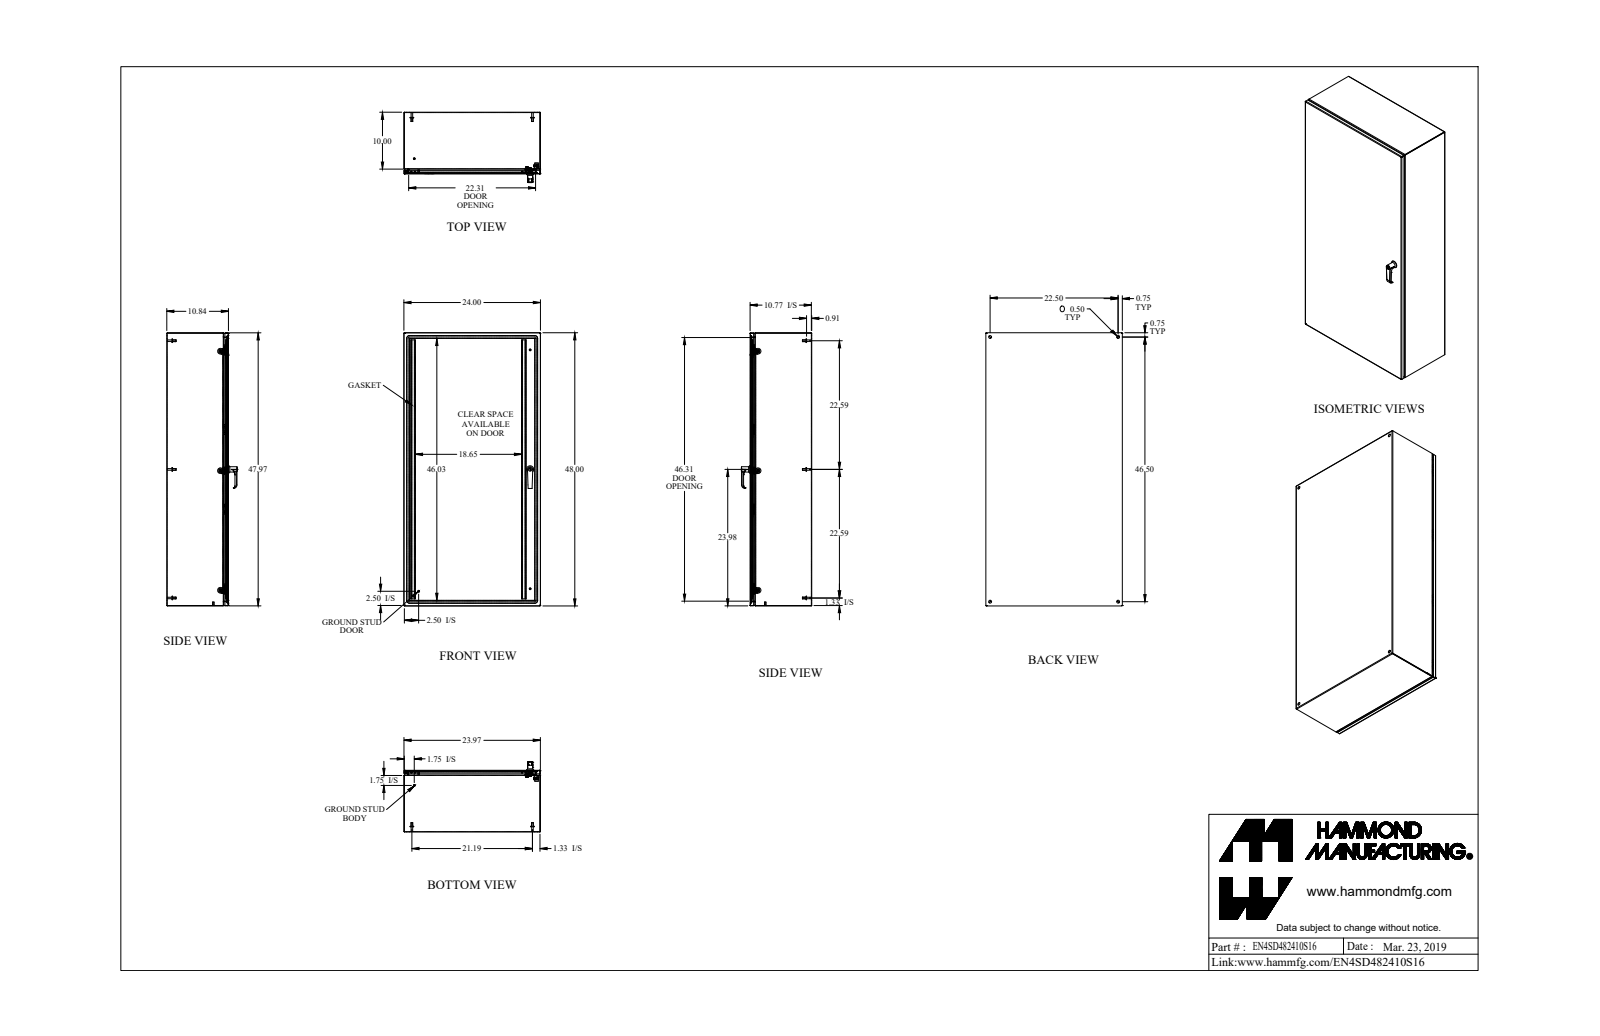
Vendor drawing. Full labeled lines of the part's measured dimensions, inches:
Part name (STEP PRODUCT): EN4SD482410S16
STEP written by: SolidWorks 2018 (AUTOMOTIVE_DESIGN)
Units: inches
Bodies: 53 solids, 1467 faces (632 planar, 536 cylindrical, 299 other)
Overall size (bounding box): 48 × 24 × 12.372
Volume: 319.5 in³ · Surface area: 8 871 in²
Round holes (diameter × count): ⌀0.176 ×6, ⌀0.5 ×4, ⌀0.196 ×3, ⌀0.25 ×3, ⌀0.265 ×3, ⌀0.413 ×3, ⌀0.256 ×2, ⌀0.313 ×2, ⌀0.394 ×2, ⌀0.172 ×1, ⌀0.24 ×1, ⌀0.242 ×1
Round bosses / shafts (diameter × count): ⌀0.313 ×8, ⌀0.25 ×7, ⌀0.625 ×6, ⌀0.375 ×6, ⌀0.275 ×6, ⌀0.156 ×6, ⌀1 ×3, ⌀0.63 ×2
Partial cylindrical surfaces — rounded edges, fillets, slot ends (radius × count): R0.036 ×20, R0.108 ×20, R0.03 ×15, R0.01 ×12, R0.048 ×12, R0.006 ×8, R0.04 ×8, R0.062 ×8
Main face-to-face distances: 0.072, 10.77, 10.698, 10.842, 23.928, 23.856, 24, 0.072, 47.928, 47.928
Hole centre spacings: 21, 21.558, 22.5, 42, 46.5, 51.657, 0.772, 0.782
